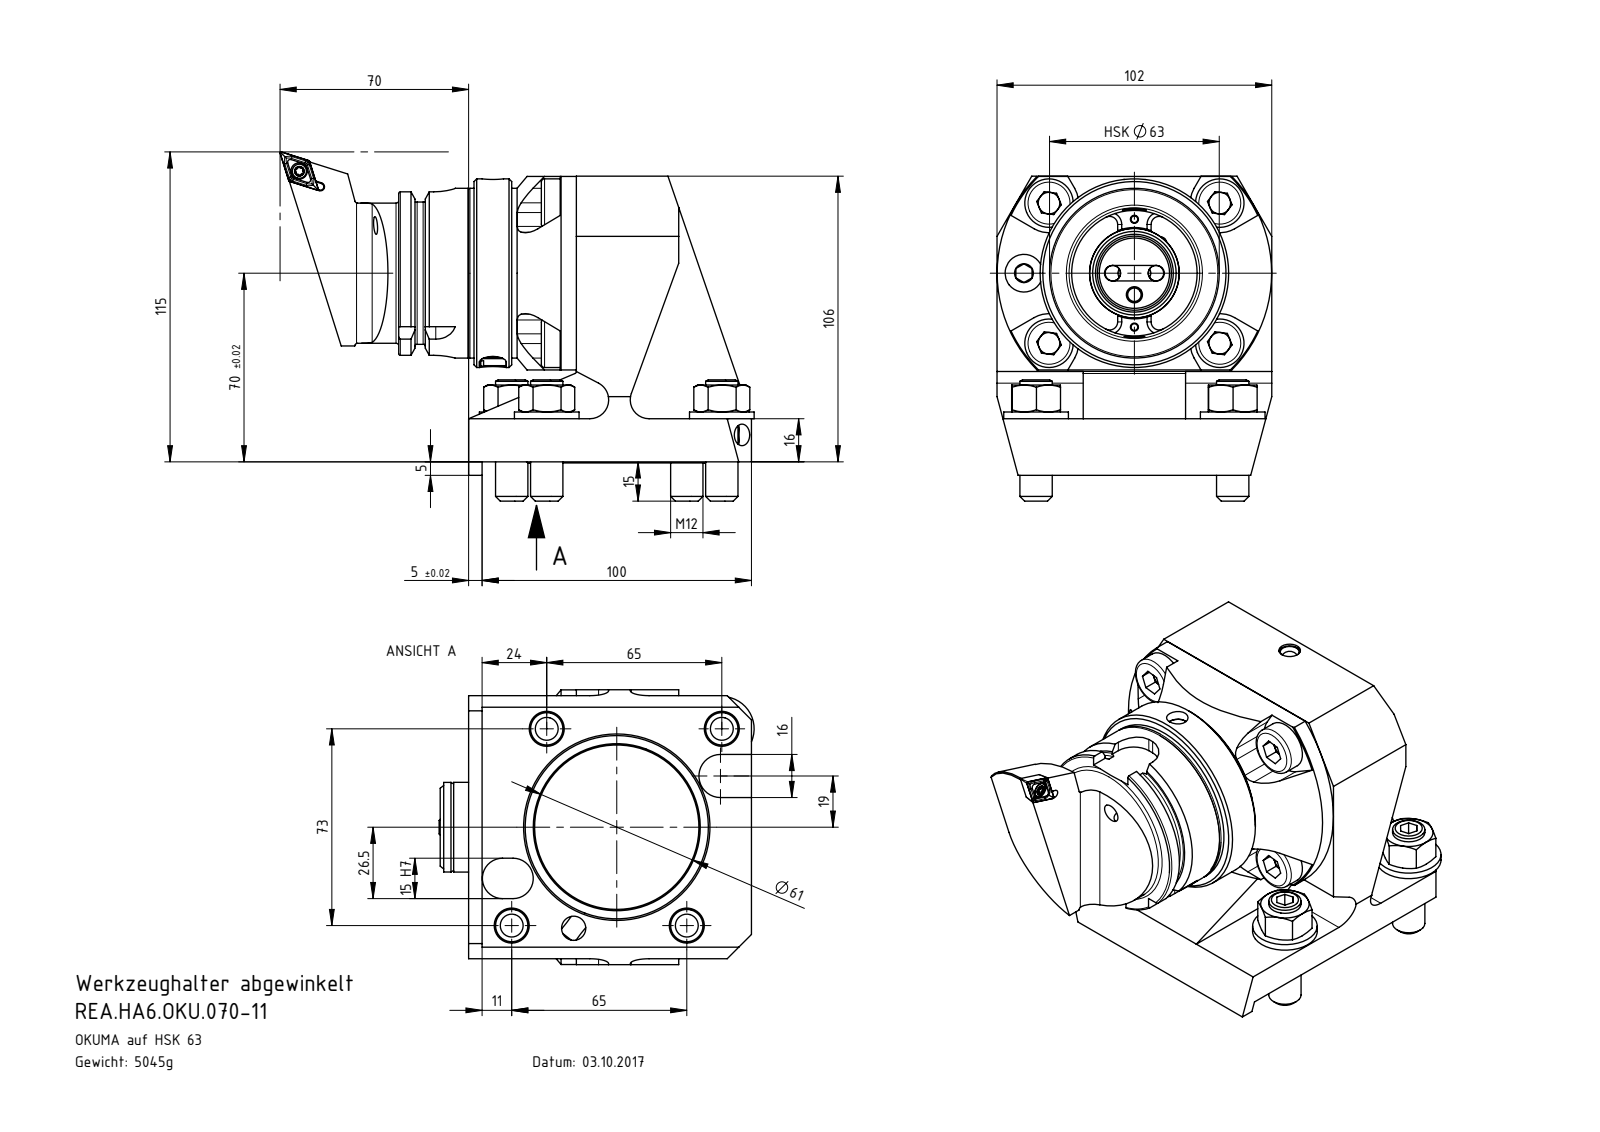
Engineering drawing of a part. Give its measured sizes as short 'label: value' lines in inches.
name: KVT_MB_600_080; HA6-ER1.001.000; ISO 4026 - M12 x 45; ISO 4032 - M12_PreviewCfg (+8 more)
written by: SolidWorks 2017 (AUTOMOTIVE_DESIGN)
unit: in
bodies: 40 solids, 1186 faces (386 planar, 365 cylindrical, 435 other)
size: 6.93 × 5.102 × 4.016
volume: 47.26 in³; area: 294 in²
holes: 8× ⌀0.402, 8× ⌀0.512, 4× ⌀0.197, 4× ⌀0.268, 4× ⌀0.472, 3× ⌀0.315, 2× ⌀0.098, 2× ⌀0.226, 2× ⌀0.228, 2× ⌀0.236, 2× ⌀0.276, 2× ⌀0.394
bosses: 4× ⌀0.945, 4× ⌀0.709, 4× ⌀0.472, 2× ⌀0.315, 1× ⌀2.756, 1× ⌀2.48, 1× ⌀2.461, 1× ⌀2.402
rounds: 12× R0.118, 8× R0.197, 6× R0.013, 6× R0.023, 6× R0.055, 6× R0.315, 5× R0.433, 4× R0.114
face distances: 0.63, 1.575, 1.26, 1.496, 2.441, 0.866, 2.756, 2.362, 0.079, 0.787
hole spacings: 1.614, 0.848, 1.27, 1.385, 1.869, 2.199, 0.315, 1.764
